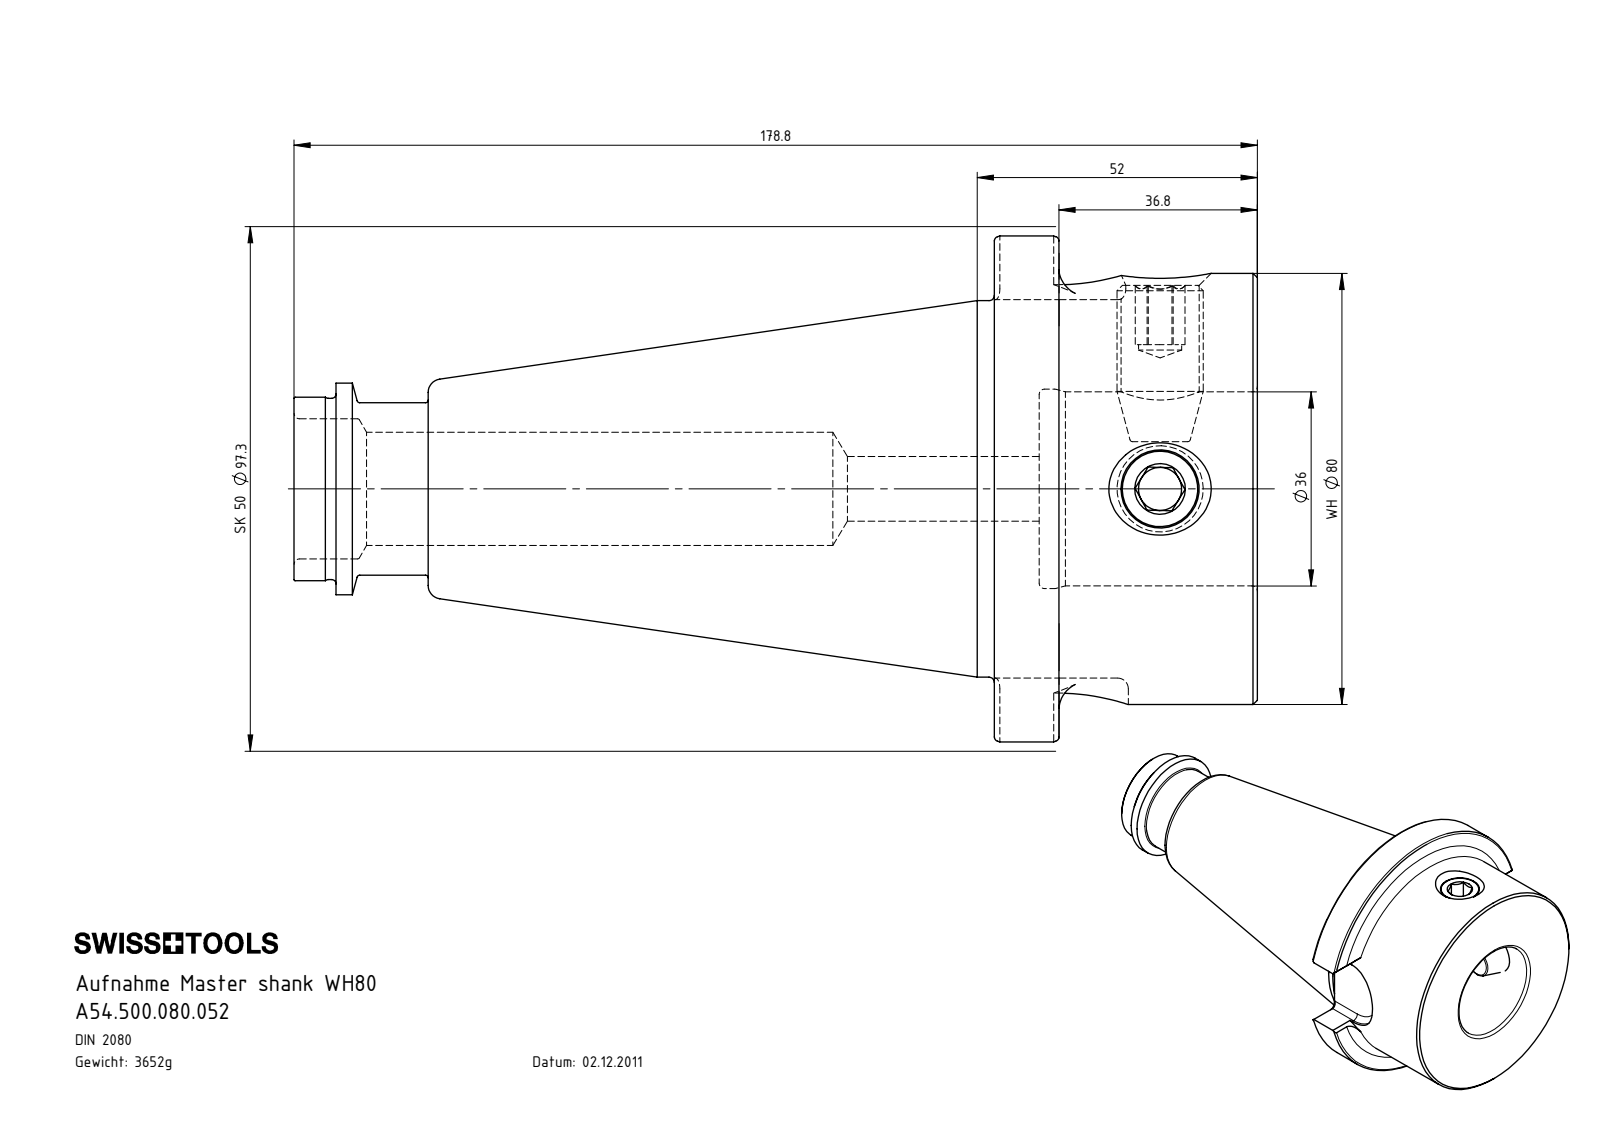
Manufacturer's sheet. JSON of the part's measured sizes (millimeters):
{"part_name": "SZ5-WH8.K01.052_B; WH8-ER1.001.029; A54.500.080.052", "step_written_by": "SolidWorks 2022 (CONFIG_CONTROL_DESIGN)", "units": "millimeters", "bodies": {"solids": 3, "faces": 168, "planar": 53, "cylindrical": 47, "other": 68}, "overall_size": [178.8, 97.3, 93.84], "volume_mm3": 465265, "surface_area_mm2": 63533, "round_holes": [[8, 2], [14.5, 2], [12, 1], [21, 1], [26, 1], [36, 1], [37, 1]], "round_bosses_or_shafts": [[16, 2], [97.3, 1], [80, 1], [69.85, 1], [39.24, 1], [34.05, 1], [33.65, 1], [32, 1]], "partial_cylinders_radius": [[2, 8], [12.85, 1]], "face_to_face_distances": [48.8, 12, 36.8, 8.3, 3.7, 40.5, 70.2, 130, 138.3, 142]}
